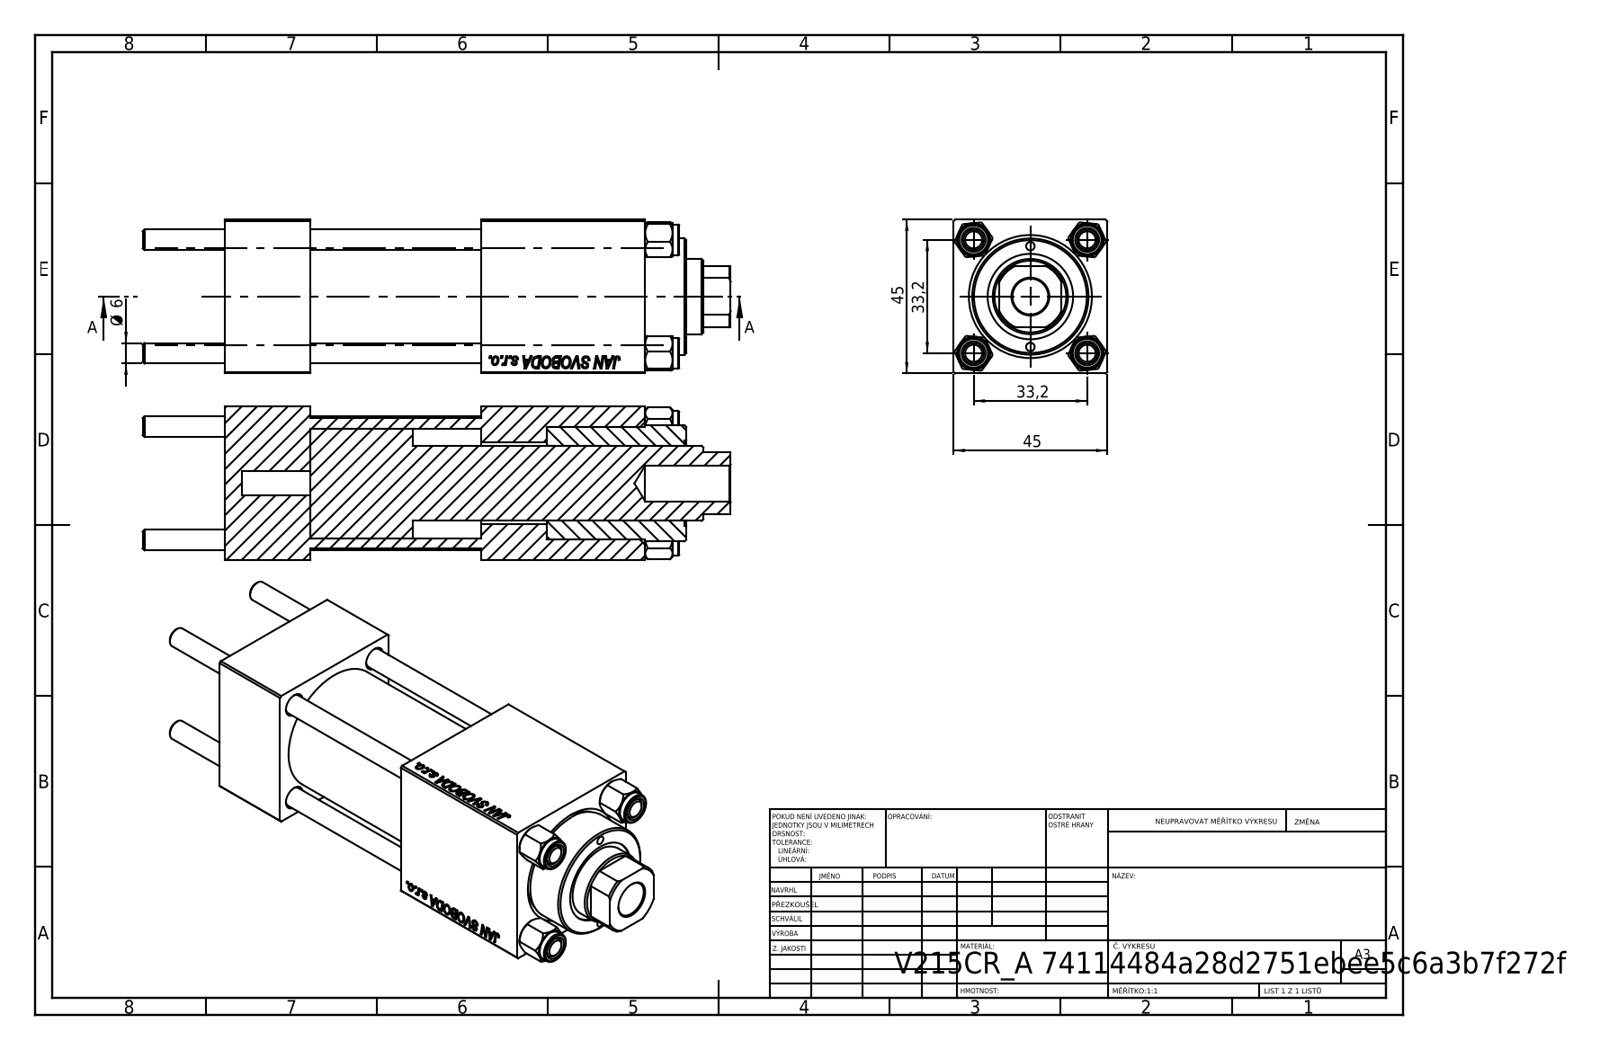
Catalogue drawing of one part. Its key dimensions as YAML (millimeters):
part_name: "V215CR_BODY_A; NUT_M5; V215CR_VCP; CR025_012_A_0_G_A_G_M_020_+#_##_TYCINKA (+1 more)"
step_written_by: "SolidWorks 2019 (CONFIG_CONTROL_DESIGN)"
units: millimeters
bodies: {solids: 11, faces: 1139, planar: 521, cylindrical: 82, other: 536}
overall_size: [172, 45, 45]
volume: 214107
surface_area: 77308
round_holes:
  - {diameter: 6, count: 4}
  - {diameter: 2.5, count: 2}
  - {diameter: 7, count: 2}
  - {diameter: 13.16, count: 2}
  - {diameter: 20, count: 2}
  - {diameter: 10.5, count: 1}
  - {diameter: 22, count: 1}
  - {diameter: 24, count: 1}
  - {diameter: 25, count: 1}
  - {diameter: 32, count: 1}
  - {diameter: 33, count: 1}
round_bosses_or_shafts:
  - {diameter: 9, count: 4}
  - {diameter: 38, count: 1}
  - {diameter: 34, count: 1}
partial_cylinders:
  - {radius: 10.5, count: 1}
face_to_face_distances: [45, 25, 123, 50, 75, 98, 48, 94.3, 69.3, 19.3]
hole_center_spacings: [16.7, 23.48, 33.2, 35.47, 14.75, 46.95, 29.5, 75.5]
